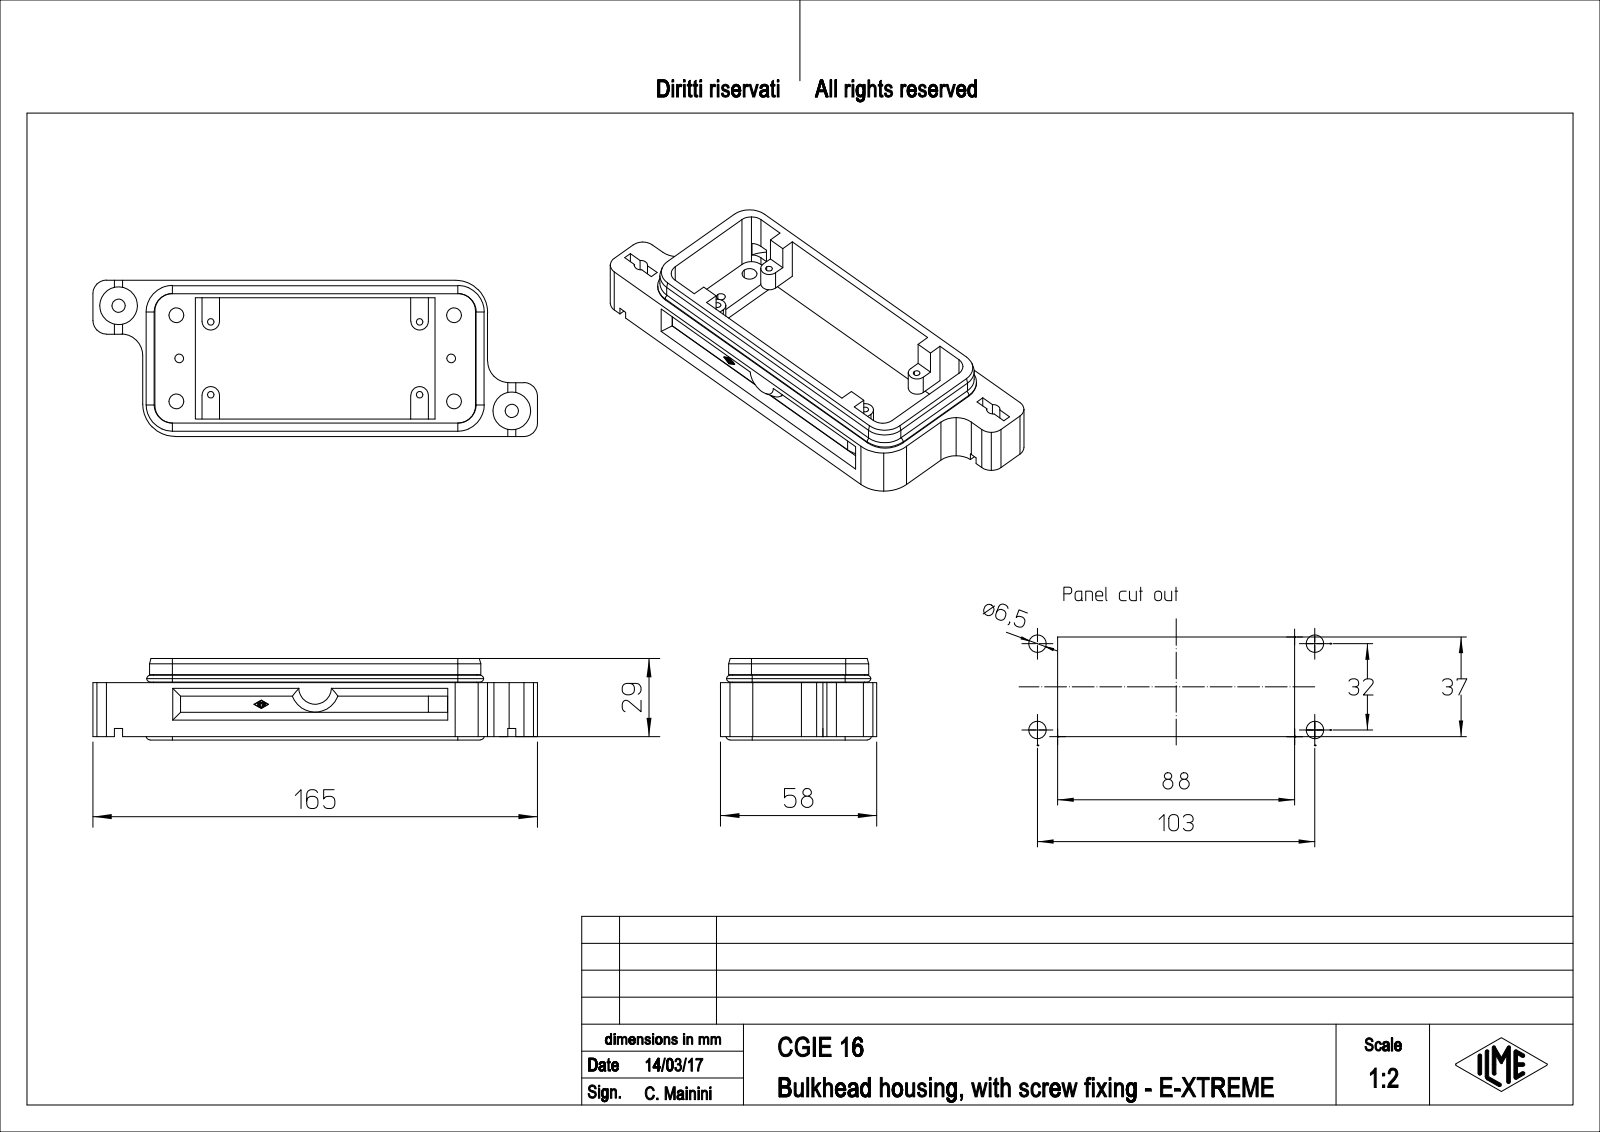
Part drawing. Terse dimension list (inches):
name: CGIE_16
written by: PTC Creo Elements/Direct Modeling 19.0E 27-Jun-2016 (C) Parametric Technology GmbH (AUTOMOTIVE_DESIGN)
unit: in
bodies: 1 solid, 304 faces (158 planar, 120 cylindrical, 26 other)
size: 6.496 × 2.283 × 1.191
volume: 4.388 in³; area: 58.84 in²
holes: 4× ⌀0.097, 4× ⌀0.217, 2× ⌀0.128, 2× ⌀0.194, 2× ⌀0.551
bosses: 4× ⌀0.098, 2× ⌀0.118
rounds: 14× R0.004, 8× R0.197, 4× R0.128, 4× R0.256, 4× R0.276, 4× R0.335, 4× R0.374, 2× R0.059
face distances: 0.256, 0.118, 2.028, 1.772, 0.787, 0.354, 0.138, 1.909, 2.165, 0.098
hole spacings: 0.511, 0.631, 0.705, 1.265, 3.554, 3.554, 3.738, 4.065
